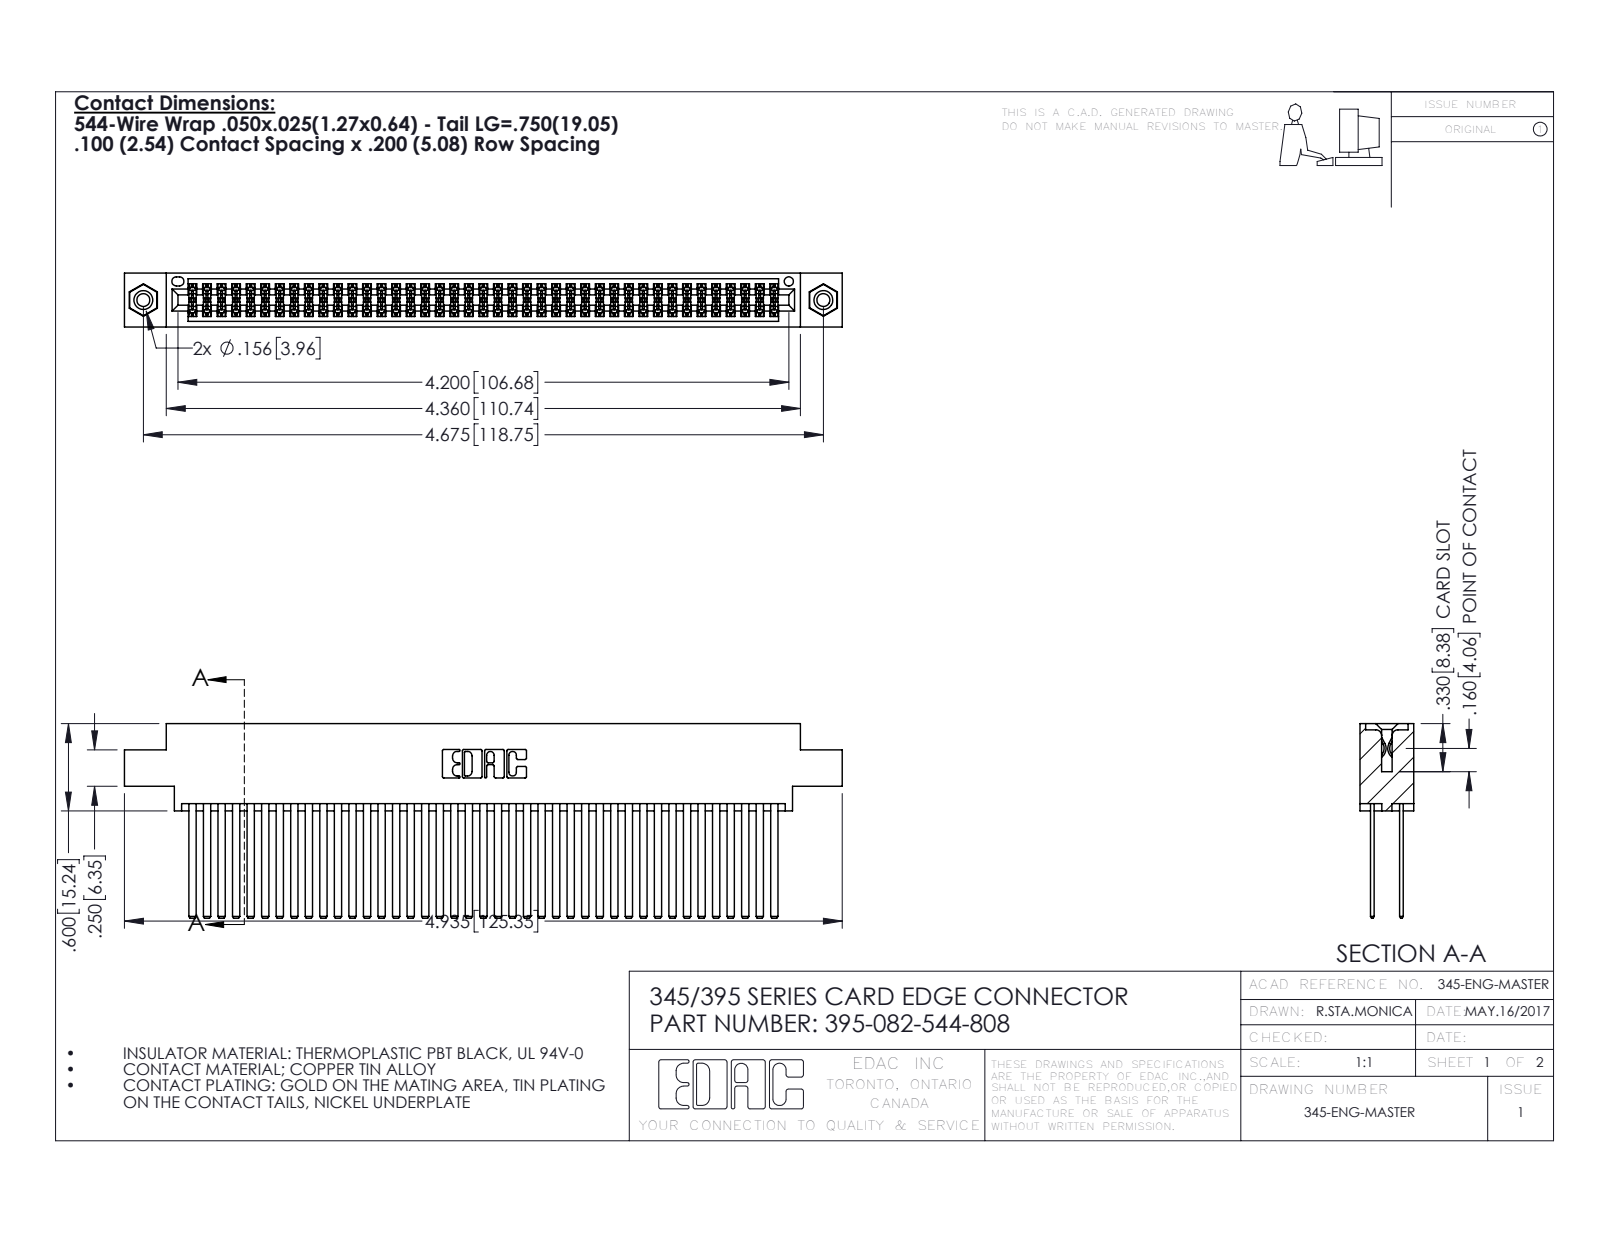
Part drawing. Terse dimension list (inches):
name: 345-292-001_345-293-144; 395-082-544-808; 345 Part_0.170 Offset - 0.156 Dia-TI; 345-250-001_345-250-003-102
written by: SolidWorks 2016 (CONFIG_CONTROL_DESIGN)
unit: in
bodies: 85 solids, 3798 faces (2494 planar, 1288 cylindrical, 16 other)
size: 4.935 × 1.337 × 0.37
volume: 0.805 in³; area: 35.67 in²
holes: 2× ⌀0.089, 2× ⌀0.125, 2× ⌀0.156, 1× ⌀0.064
bosses: 2× ⌀0.155
rounds: 123× R0.006, 22× R0.01, 6× R0.007, 6× R0.031, 3× R0.026, 2× R0.014, 2× R0.019, 2× R0.022
face distances: 0.2, 0.025, 0.072, 0.098, 0.272, 0.298, 0.225, 0.175, 0.37, 0.15
hole spacings: 0.27, 4.439, 4.675
